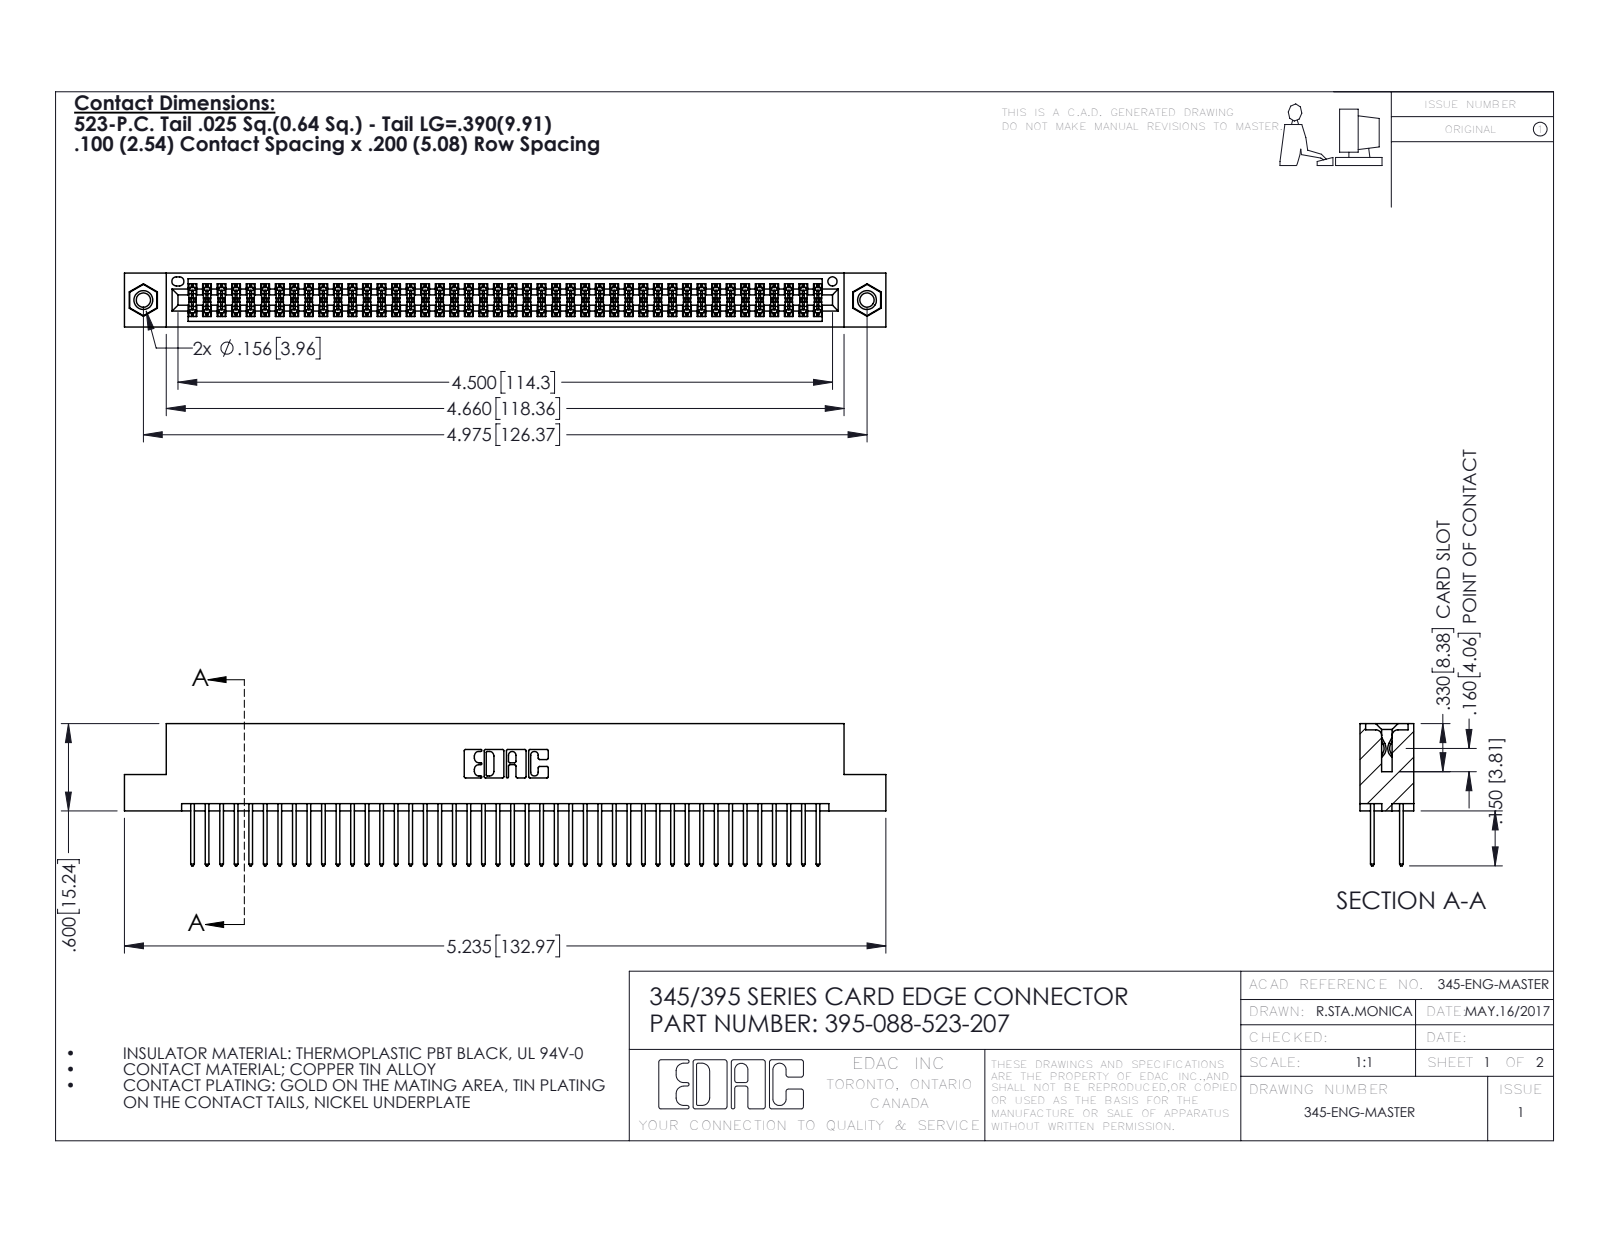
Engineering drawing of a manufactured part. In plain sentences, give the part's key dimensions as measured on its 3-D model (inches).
The part is named "395-088-523-207; 345 Part_Flush Mounting Lugs - 0.156 Dia-TI; 345-250-001_345-250-005-103; 345-292-001_345-293-123". Its 3-D file was written by "SolidWorks 2016 (CONFIG_CONTROL_DESIGN)". It is 91 solids with 4586 faces: 3016 planar, 1554 cylindrical and 16 other. Overall it measures 5.235 by 0.977 by 0.37 inches. Its volume is 0.8 cubic inches and its surface area 31.38 square inches. Round holes: 2 of diameter 0.098, 2 of diameter 0.125, 2 of diameter 0.156, 1 of diameter 0.064. Round bosses or shafts: 2 of diameter 0.155. Partial cylindrical surfaces (rounded edges, fillets, slot ends): 132 of radius 0.006, 88 of radius 0.01, 22 of radius 0.01, 6 of radius 0.007, 6 of radius 0.031, 3 of radius 0.026, 2 of radius 0.014, 2 of radius 0.019. The main face-to-face distances are 0.072, 0.298, 0.2, 0.098, 0.272, 0.025, 0.37, 0.225, 0.175, 0.149. The hole center spacings are 0.27, 4.739, 4.975.
